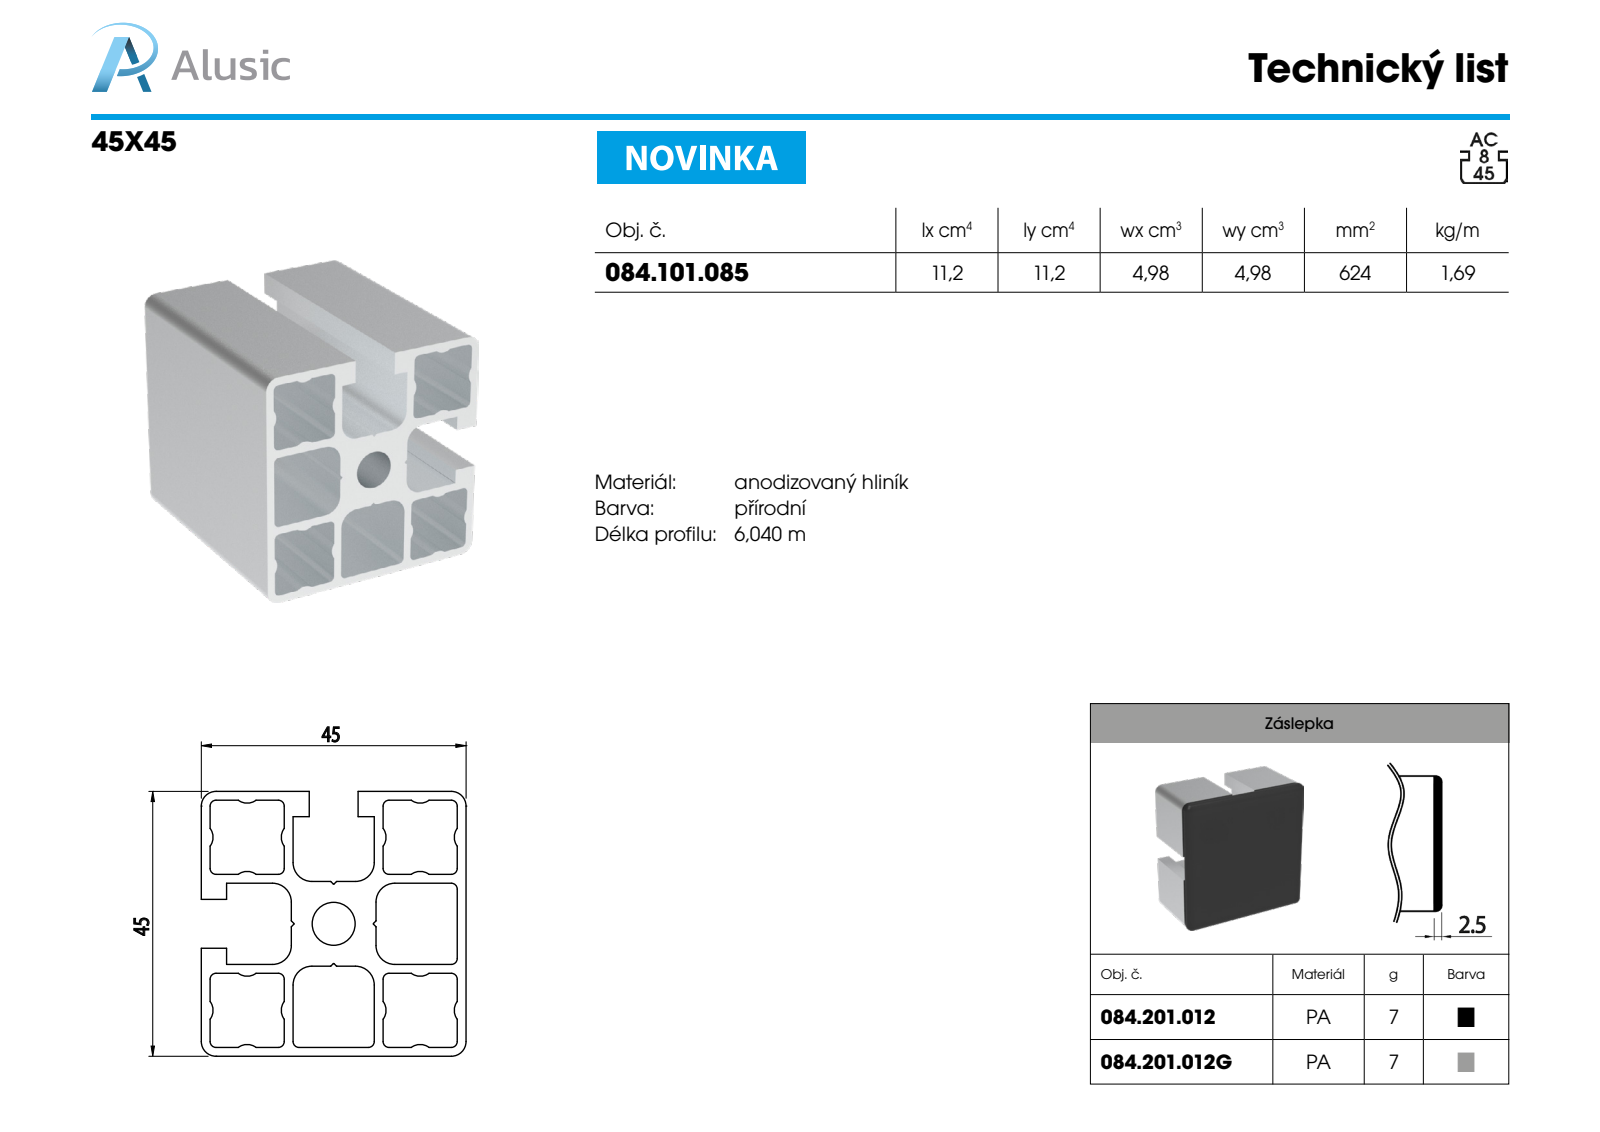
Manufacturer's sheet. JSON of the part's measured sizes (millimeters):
{"part_name": "084.101.085", "step_written_by": "SolidWorks 2018 (AUTOMOTIVE_DESIGN)", "units": "millimeters", "bodies": {"solids": 1, "faces": 141, "planar": 74, "cylindrical": 67, "other": 0}, "overall_size": [100, 45, 45], "volume_mm3": 62396, "surface_area_mm2": 59168, "round_holes": [[7.3, 1]], "partial_cylinders_radius": [[1, 20], [2.5, 20], [0.1, 12], [3.2, 8]], "face_to_face_distances": [14.1, 1.5, 29.4, 15.6, 15.3, 43.5, 45, 27.9, 30.9, 12.6]}
